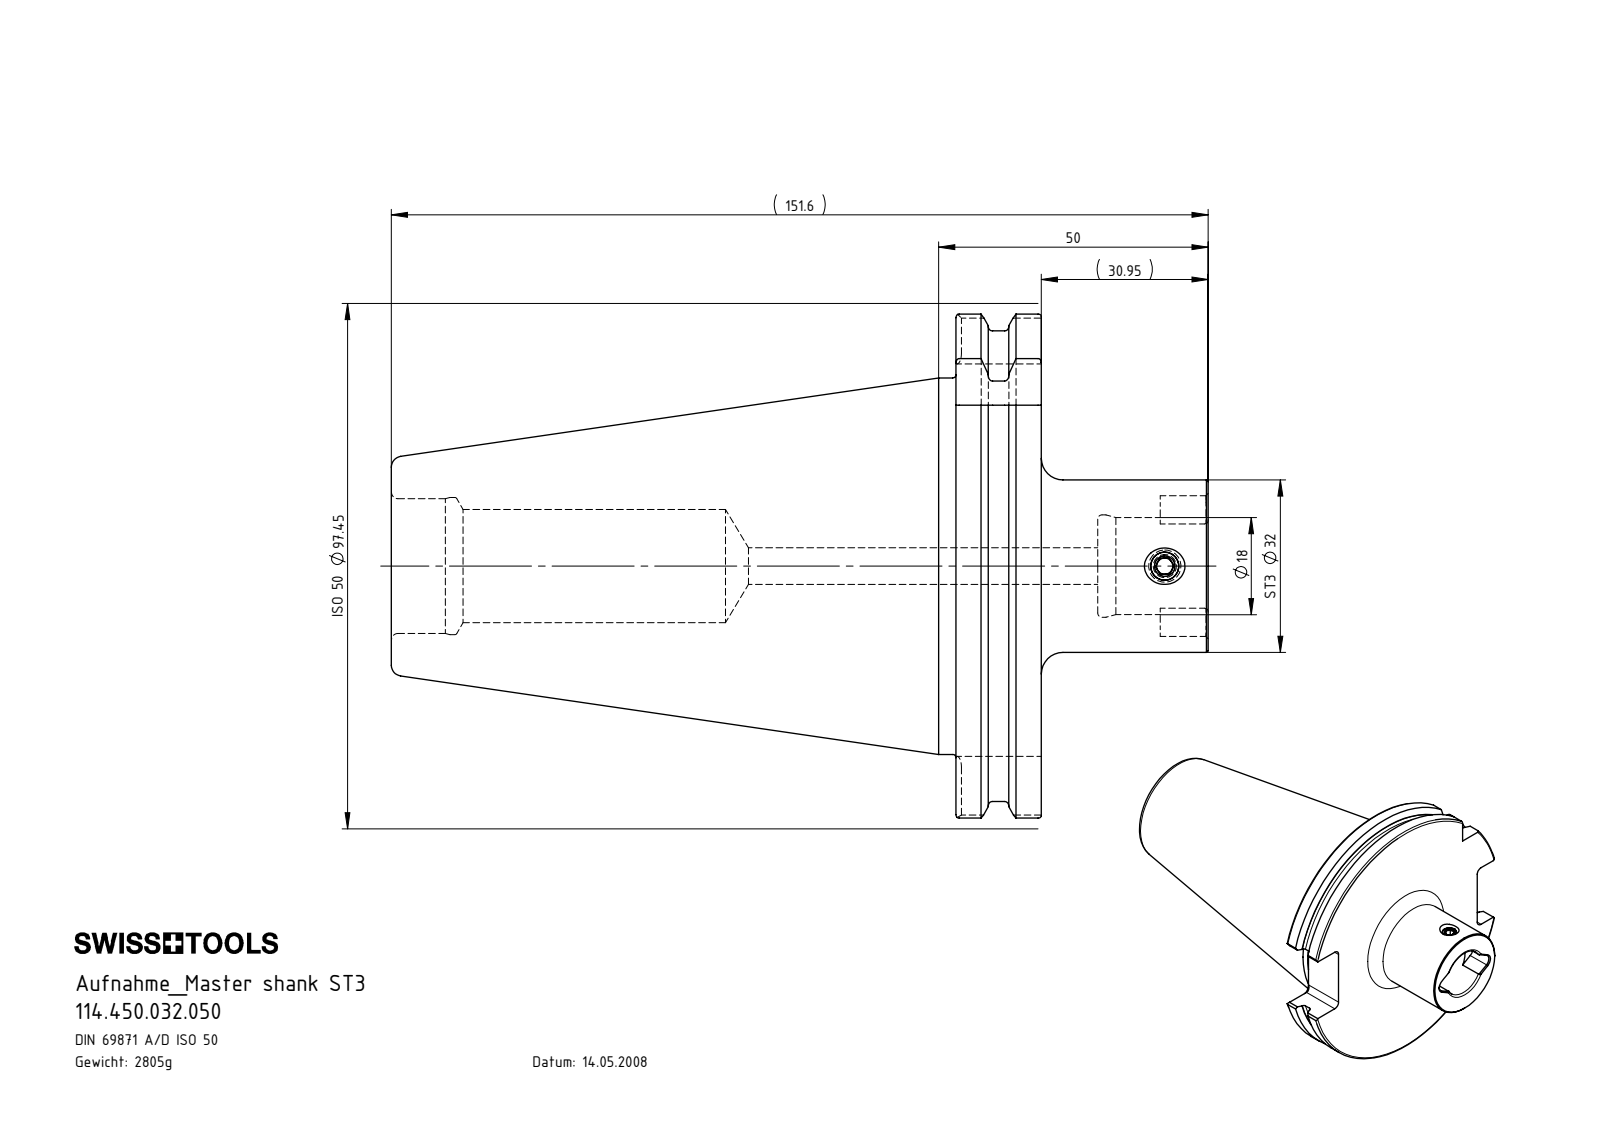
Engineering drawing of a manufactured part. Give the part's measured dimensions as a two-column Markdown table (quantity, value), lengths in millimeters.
| quantity | value |
| --- | --- |
| part name | ST3-ER1.001.008_A; SK5-ST3.K01.050_B; SK5.ST3.K01.050 |
| STEP written by | SolidWorks 2017 (AUTOMOTIVE_DESIGN) |
| units | millimeters |
| bodies | 2 solids, 126 faces (54 planar, 30 cylindrical, 42 other) |
| overall size | 151.6 × 97.45 × 93.51 |
| volume | 357 296 mm³ |
| surface area | 45 491 mm² |
| round holes (diameter × count) | 3 × 1, 5.25 × 1, 6.8 × 1, 18 × 1, 19 × 1, 21 × 1, 25 × 1, 25.45 × 1 |
| round bosses / shafts (diameter × count) | 91 × 1, 69.85 × 1, 32 × 1, 6 × 1 |
| partial cylindrical surfaces (radius × count) | 2 × 8, 2.5 × 2, 48.73 × 1 |
| main face-to-face distances | 15.85, 104.8, 120.65, 151.6, 46.8, 30.95, 72.8, 25.7, 131.1, 26.3 |
